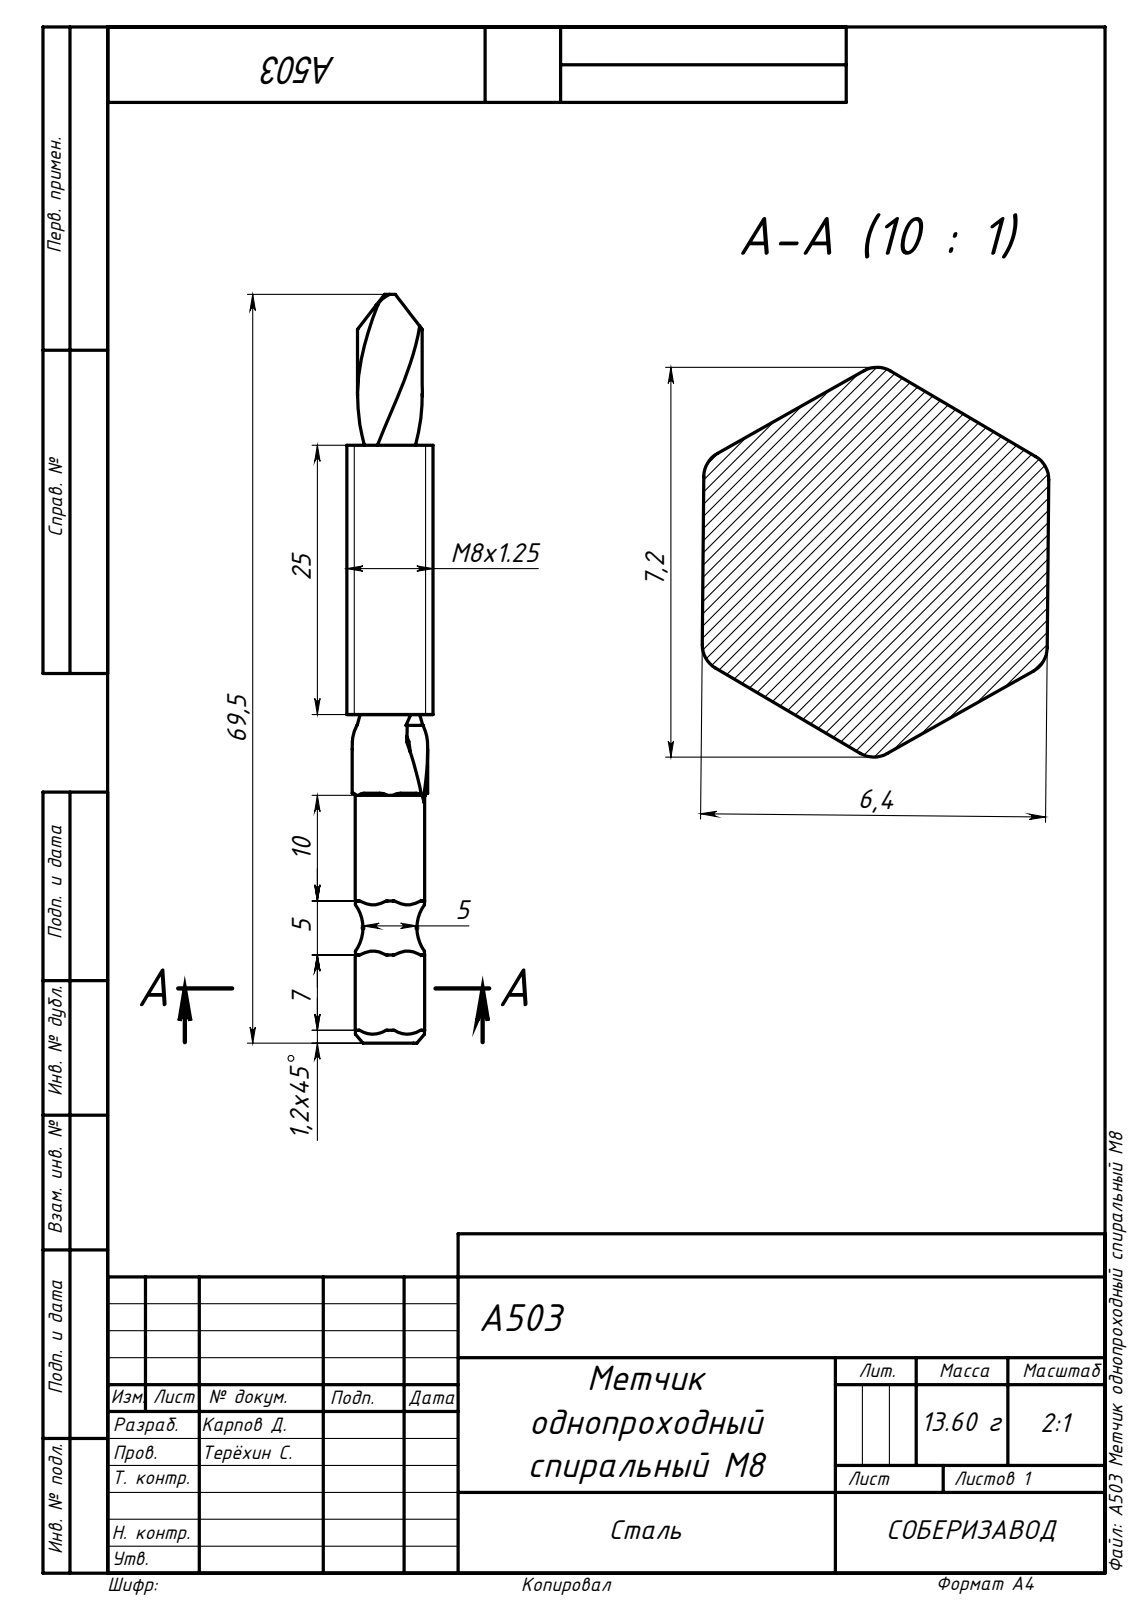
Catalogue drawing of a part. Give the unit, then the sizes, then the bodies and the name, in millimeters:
Units: millimetres
Overall size (bounding box): 69.5 × 8 × 8
Round holes (diameter × count): ⌀2 ×1
Round bosses / shafts (diameter × count): ⌀8 ×1, ⌀7 ×1
Partial cylindrical surfaces — rounded edges, fillets, slot ends (radius × count): R0.2 ×6, R0.5 ×6
Main face-to-face distances: 6.4, 21.96, 240.13, 8.76, 25, 15.56, 28.36, 15.16, 246.53, 233.73
Volume: 2 324 mm³ · Surface area: 1 711 mm²
Bodies: 1 solid, 113 faces (63 planar, 26 cylindrical, 24 other)
Part name (STEP PRODUCT): A503 Метчик однопроходный спиральный М8
STEP written by: SolidWorks 2021 (AUTOMOTIVE_DESIGN)
